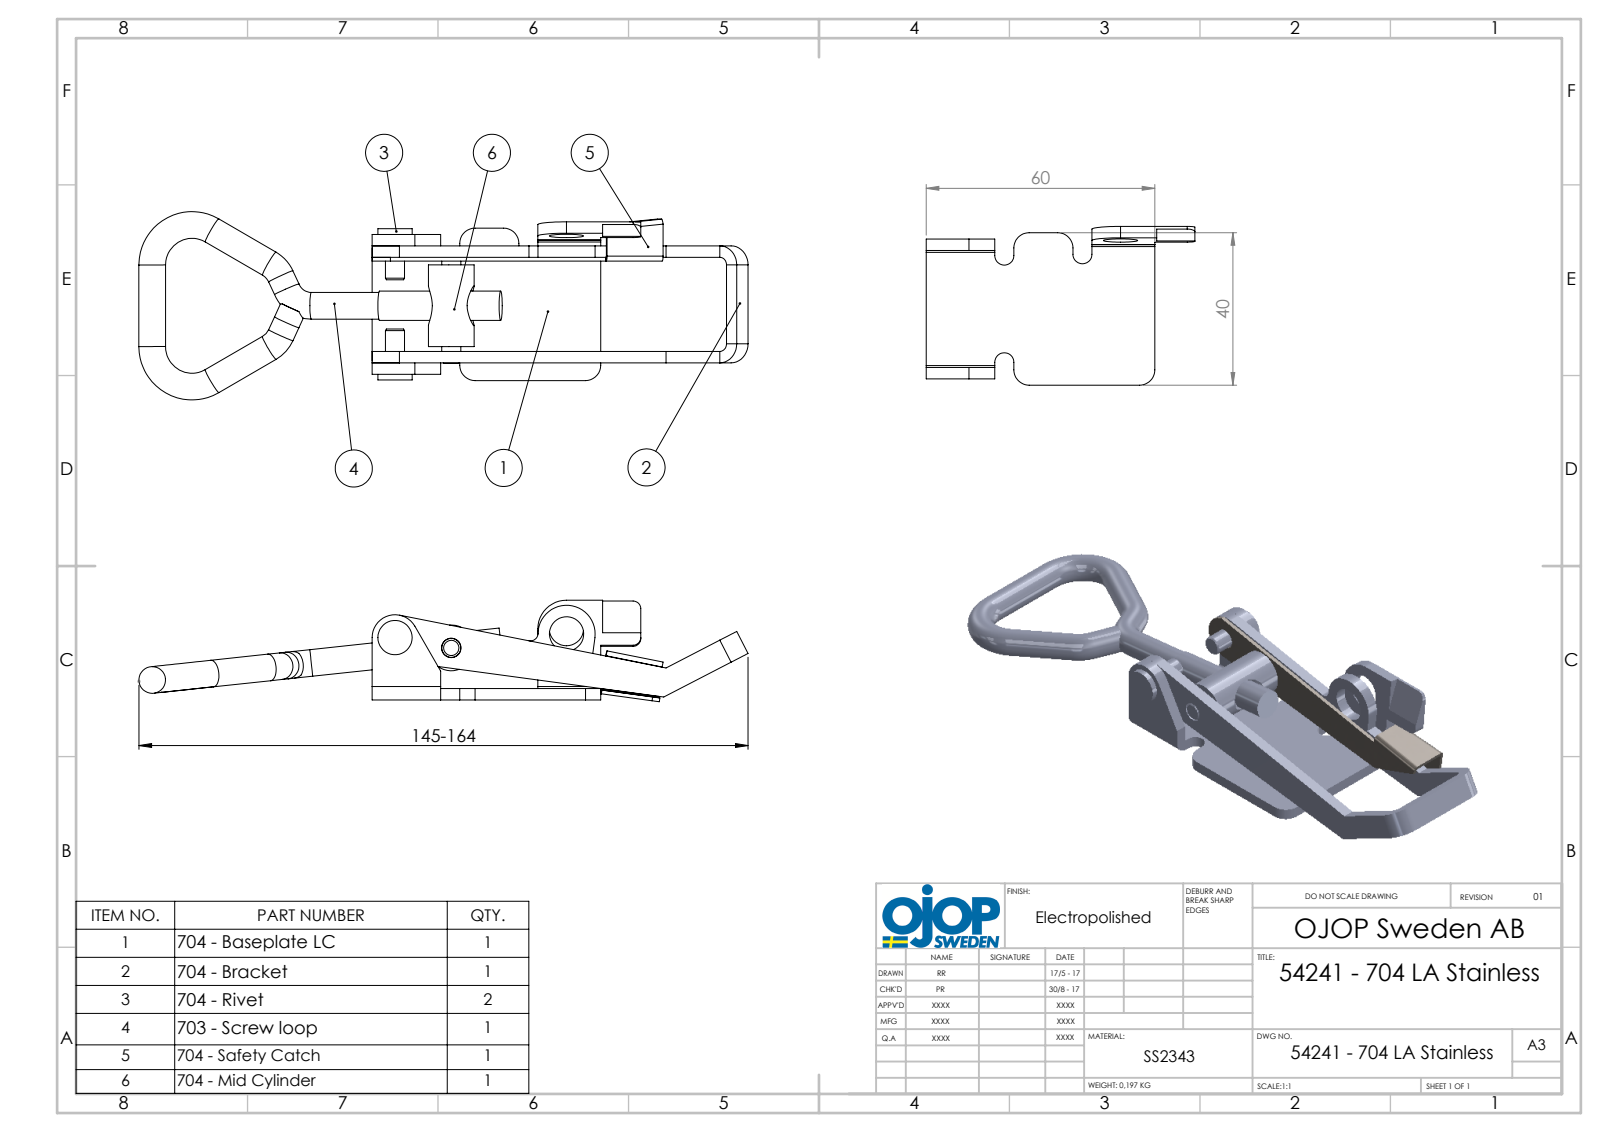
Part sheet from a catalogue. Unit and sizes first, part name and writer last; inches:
Units: inches
Overall size (bounding box): 6.296 × 1.945 × 1.048
Round holes (diameter × count): ⌀0.201 ×2, ⌀0.354 ×2, ⌀0.213 ×1, ⌀0.283 ×1, ⌀0.303 ×1
Round bosses / shafts (diameter × count): ⌀0.276 ×4, ⌀0.197 ×2, ⌀0.472 ×1, ⌀0.354 ×1, ⌀0.303 ×1
Partial cylindrical surfaces — rounded edges, fillets, slot ends (radius × count): R0.079 ×5, R0.157 ×4, R0.012 ×3, R0.02 ×3, R0.051 ×3, R0.098 ×3, R0.138 ×3, R0.197 ×2
Main face-to-face distances: 0.118, 1.091, 1.209, 0.039, 0.972, 0.157, 0.933, 1.051, 0.236, 1.327
Hole centre spacings: 0.591, 1.2, 1.774
Volume: 1.583 in³ · Surface area: 33 in²
Bodies: 7 solids, 227 faces (106 planar, 89 cylindrical, 32 other)
Part name (STEP PRODUCT): 703 - Skruvögla; 704 - Safety Catch; 704 - Mid Cylinder; 54241 - 704 LA Stainless (+3 more)
STEP written by: SolidWorks 2015 (AUTOMOTIVE_DESIGN)
